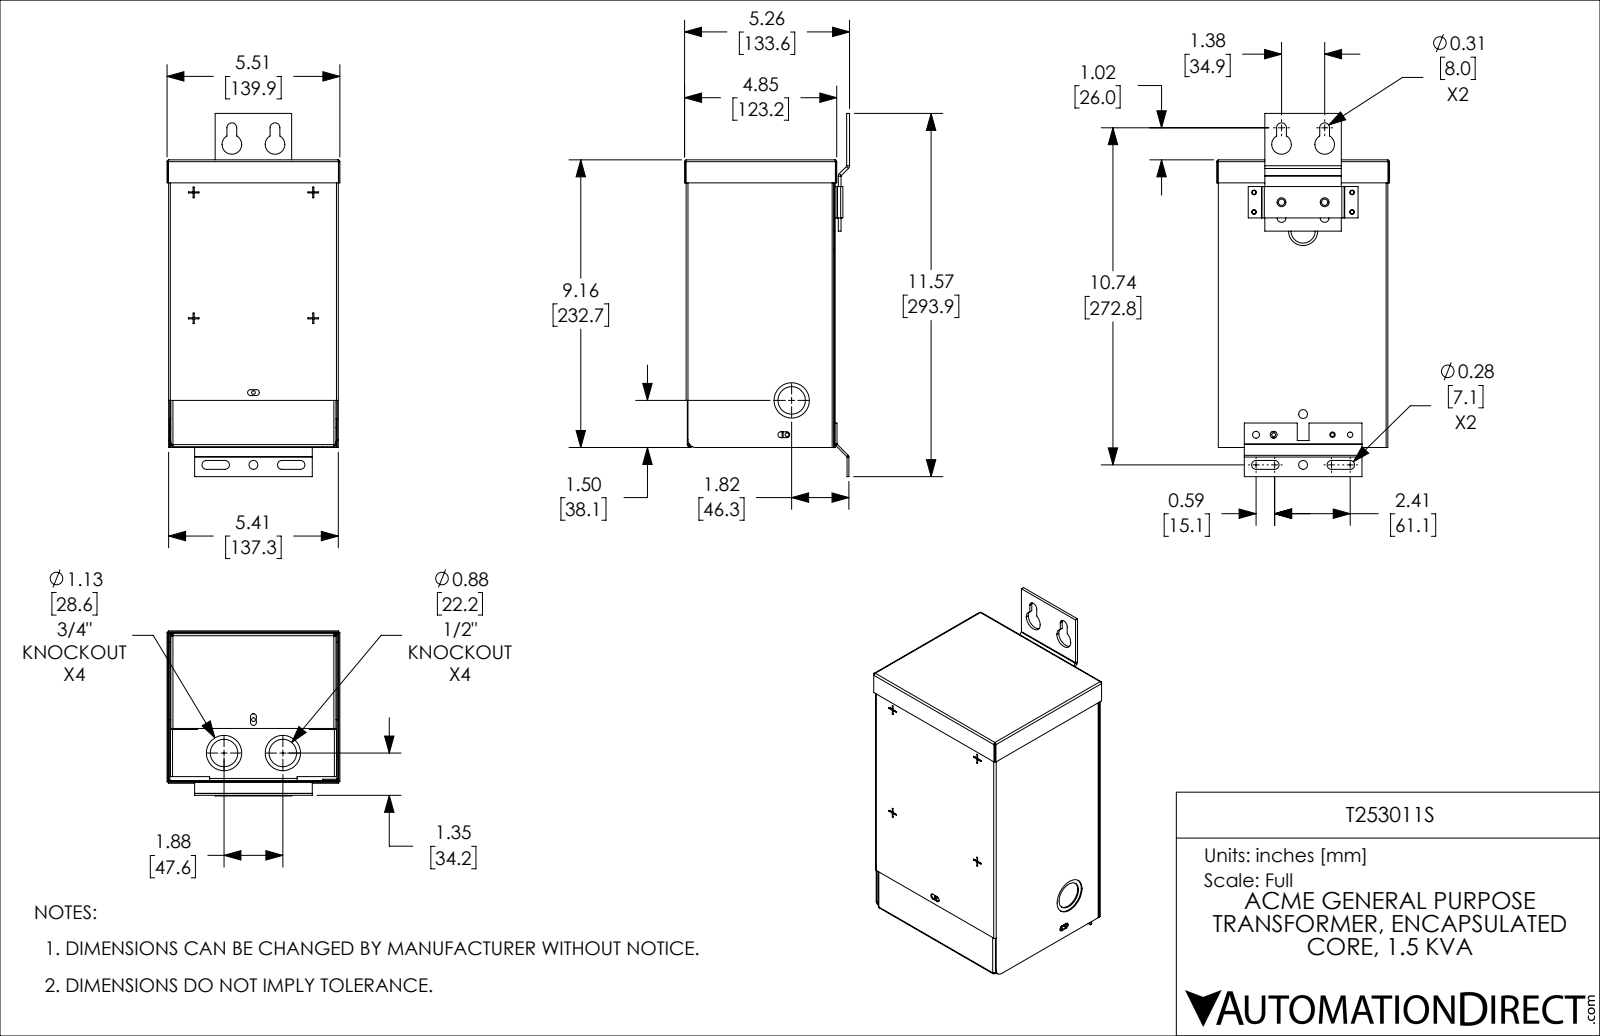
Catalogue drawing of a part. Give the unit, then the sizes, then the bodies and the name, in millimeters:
Units: millimetres
Overall size (bounding box): 293.87 × 139.9 × 133.57
Round holes (diameter × count): ⌀7.14 ×6, ⌀3.05 ×5, ⌀22.22 ×3, ⌀28.57 ×3, ⌀4.37 ×2, ⌀4.76 ×2, ⌀5.11 ×2, ⌀5.56 ×2, ⌀15.88 ×2
Round bosses / shafts (diameter × count): ⌀29.79 ×1, ⌀23.44 ×1
Partial cylindrical surfaces — rounded edges, fillets, slot ends (radius × count): R0.51 ×10, R2.38 ×10, R0.79 ×8, R1.42 ×8, R1.7 ×8, R0.38 ×4, R1.9 ×4, R3.57 ×4
Main face-to-face distances: 0.91, 119.74, 136.41, 118.83, 135.5, 137.32, 120.65, 231.14, 1.29, 2.2
Hole centre spacings: 34.92, 12.7, 14.29, 29.09, 34.08, 35.98, 37.16, 41.6
Volume: 177 414 mm³ · Surface area: 368 059 mm²
Bodies: 7 solids, 521 faces (329 planar, 152 cylindrical, 40 other)
Part name (STEP PRODUCT): T253011S
STEP written by: SolidWorks 2021 (CONFIG_CONTROL_DESIGN)
